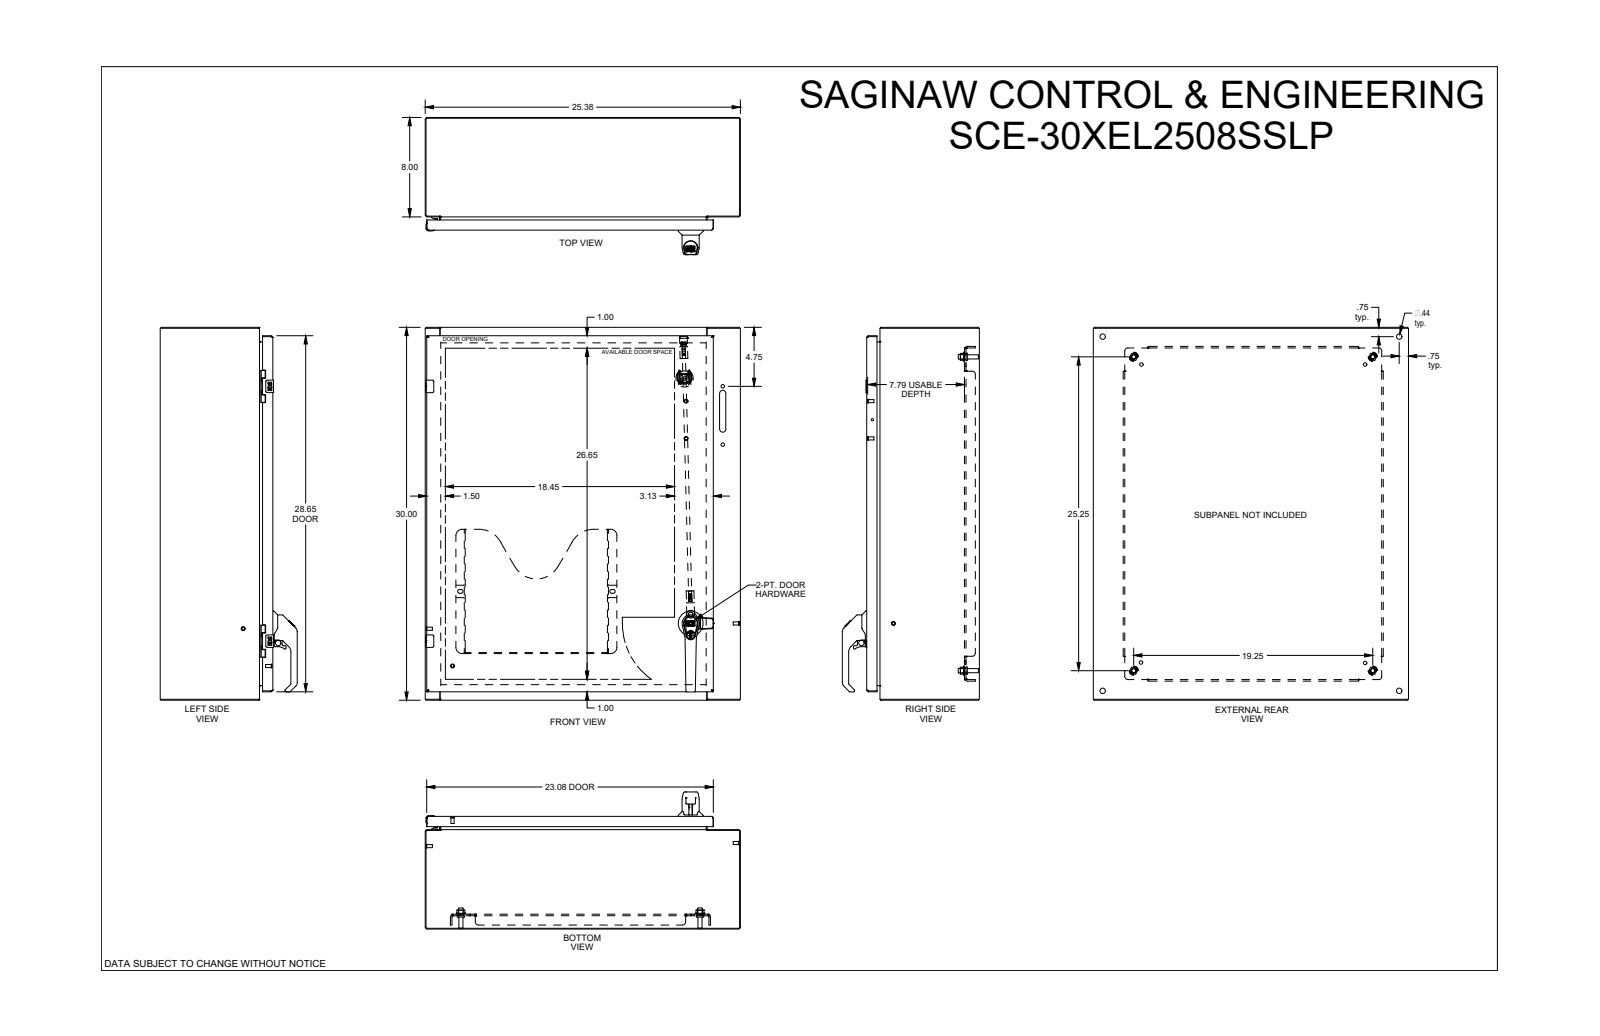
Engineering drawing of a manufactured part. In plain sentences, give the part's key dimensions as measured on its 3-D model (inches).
The part is named "SCE-30XEL2508SSLP". Its 3-D file was written by "SolidWorks 2019 (CONFIG_CONTROL_DESIGN)". It is 67 solids with 4628 faces: 1743 planar, 1218 cylindrical and 1667 other. Overall it measures 30 by 25.375 by 11.036 inches. Its volume is 312.6 cubic inches and its surface area 7 139 square inches. Round holes: 6 of diameter 0.281, 5 of diameter 0.266, 4 of diameter 0.172, 4 of diameter 0.205, 4 of diameter 0.244, 4 of diameter 0.367, 4 of diameter 0.437, 4 of diameter 0.5, 3 of diameter 0.25, 3 of diameter 0.25, 3 of diameter 0.375, 2 of diameter 0.138. Round bosses or shafts: 8 of diameter 0.248, 6 of diameter 0.17, 4 of diameter 0.366, 4 of diameter 0.332, 4 of diameter 0.25, 3 of diameter 0.563, 3 of diameter 0.196, 2 of diameter 0.341. Partial cylindrical surfaces (rounded edges, fillets, slot ends): 69 of radius 0.03, 58 of radius 0.015, 36 of radius 0.01, 36 of radius 0.02, 34 of radius 0.02, 31 of radius 0.04, 30 of radius 0.039, 26 of radius 0.005. The main face-to-face distances are 0.075, 8.993, 8.918, 9.068, 1.125, 1.2, 7.868, 7.793, 0.125, 7.918. The hole center spacings are 20.5, 0.985, 0.02, 4.493, 0.472, 0.725, 0.854, 0.866.
